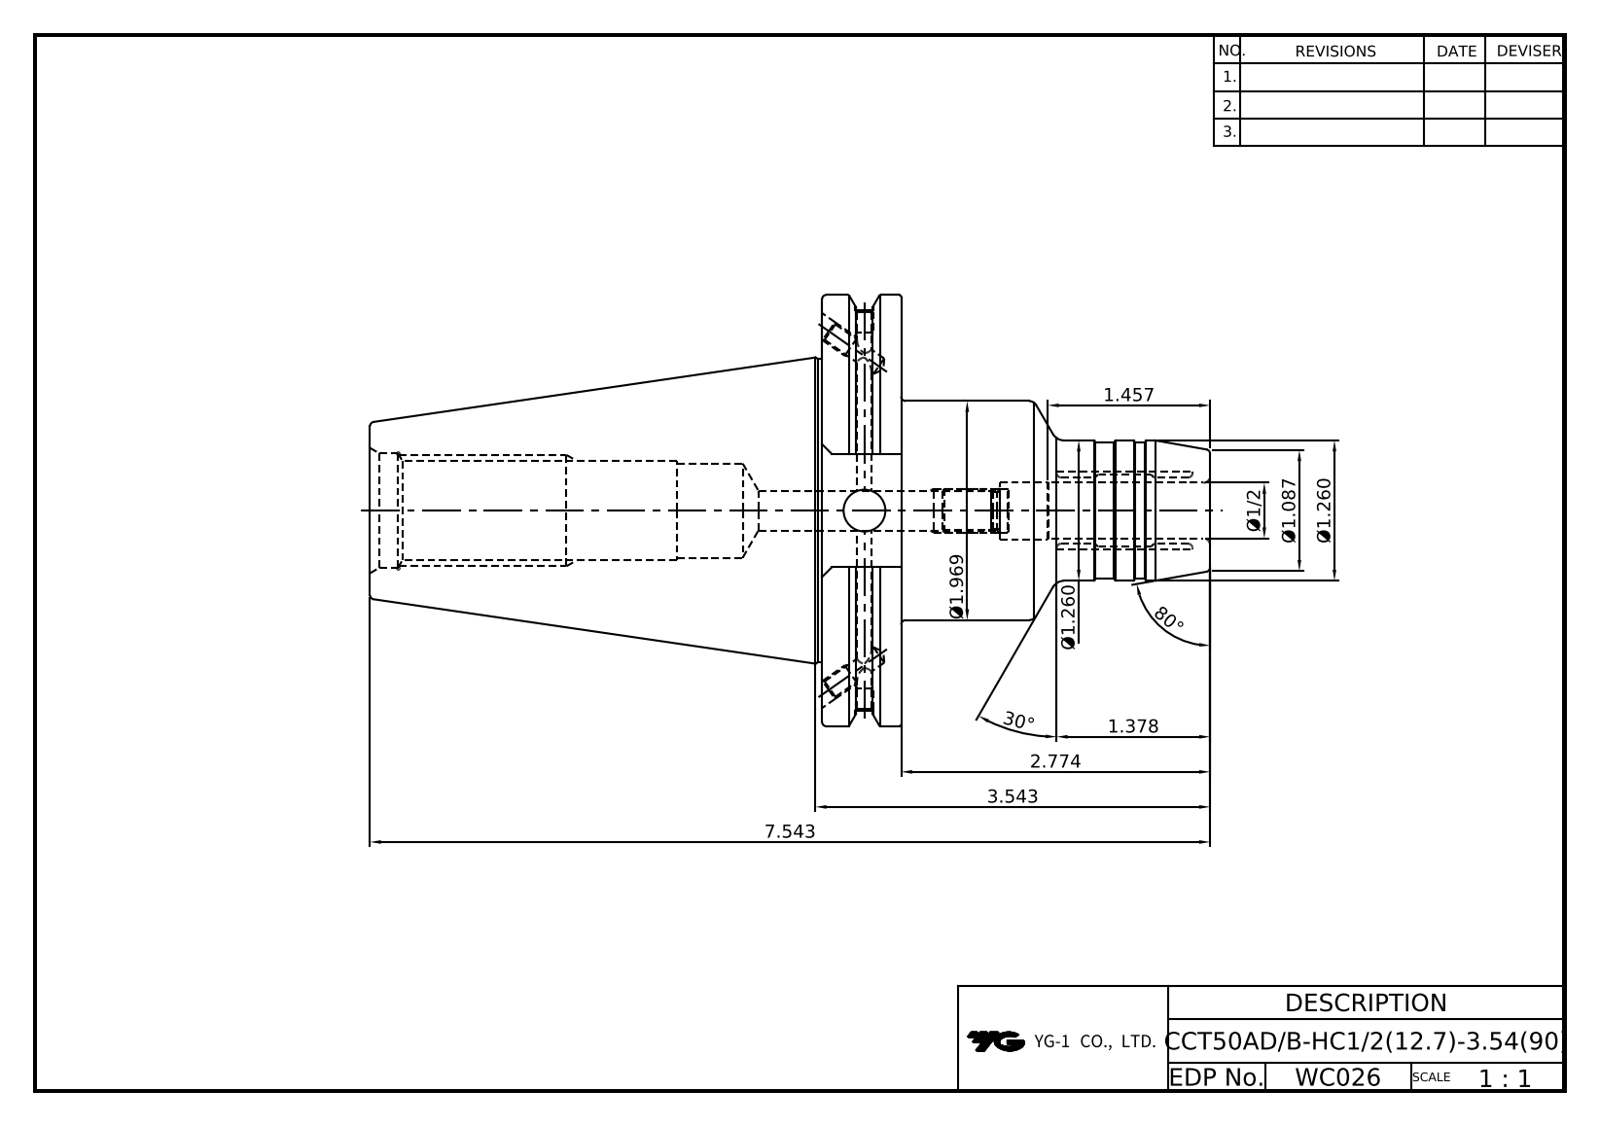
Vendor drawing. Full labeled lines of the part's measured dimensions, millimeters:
Part name (STEP PRODUCT): CCT50ADB-HC12.7-90
STEP written by: Autodesk Inventor 2022 (AUTOMOTIVE_DESIGN)
Units: millimetres
Bodies: 1 solid, 108 faces (38 planar, 32 cylindrical, 38 other)
Overall size (bounding box): 191.6 × 98.42 × 94.69
Volume: 420 318 mm³ · Surface area: 54 976 mm²
Round holes (diameter × count): ⌀3.24 ×2, ⌀4.13 ×2, ⌀4.2 ×2, ⌀5 ×2, ⌀8.92 ×1, ⌀9.53 ×1, ⌀12.7 ×1, ⌀13.2 ×1, ⌀21.5 ×1, ⌀21.97 ×1, ⌀26.2 ×1
Round bosses / shafts (diameter × count): ⌀98.42 ×1, ⌀91.29 ×1, ⌀69.25 ×1, ⌀50 ×1, ⌀32 ×1, ⌀31 ×1
Main face-to-face distances: 17.55, 103.1, 120.65, 191.6, 88.5, 70.95, 73.03, 25.9, 103.5, 0.4
